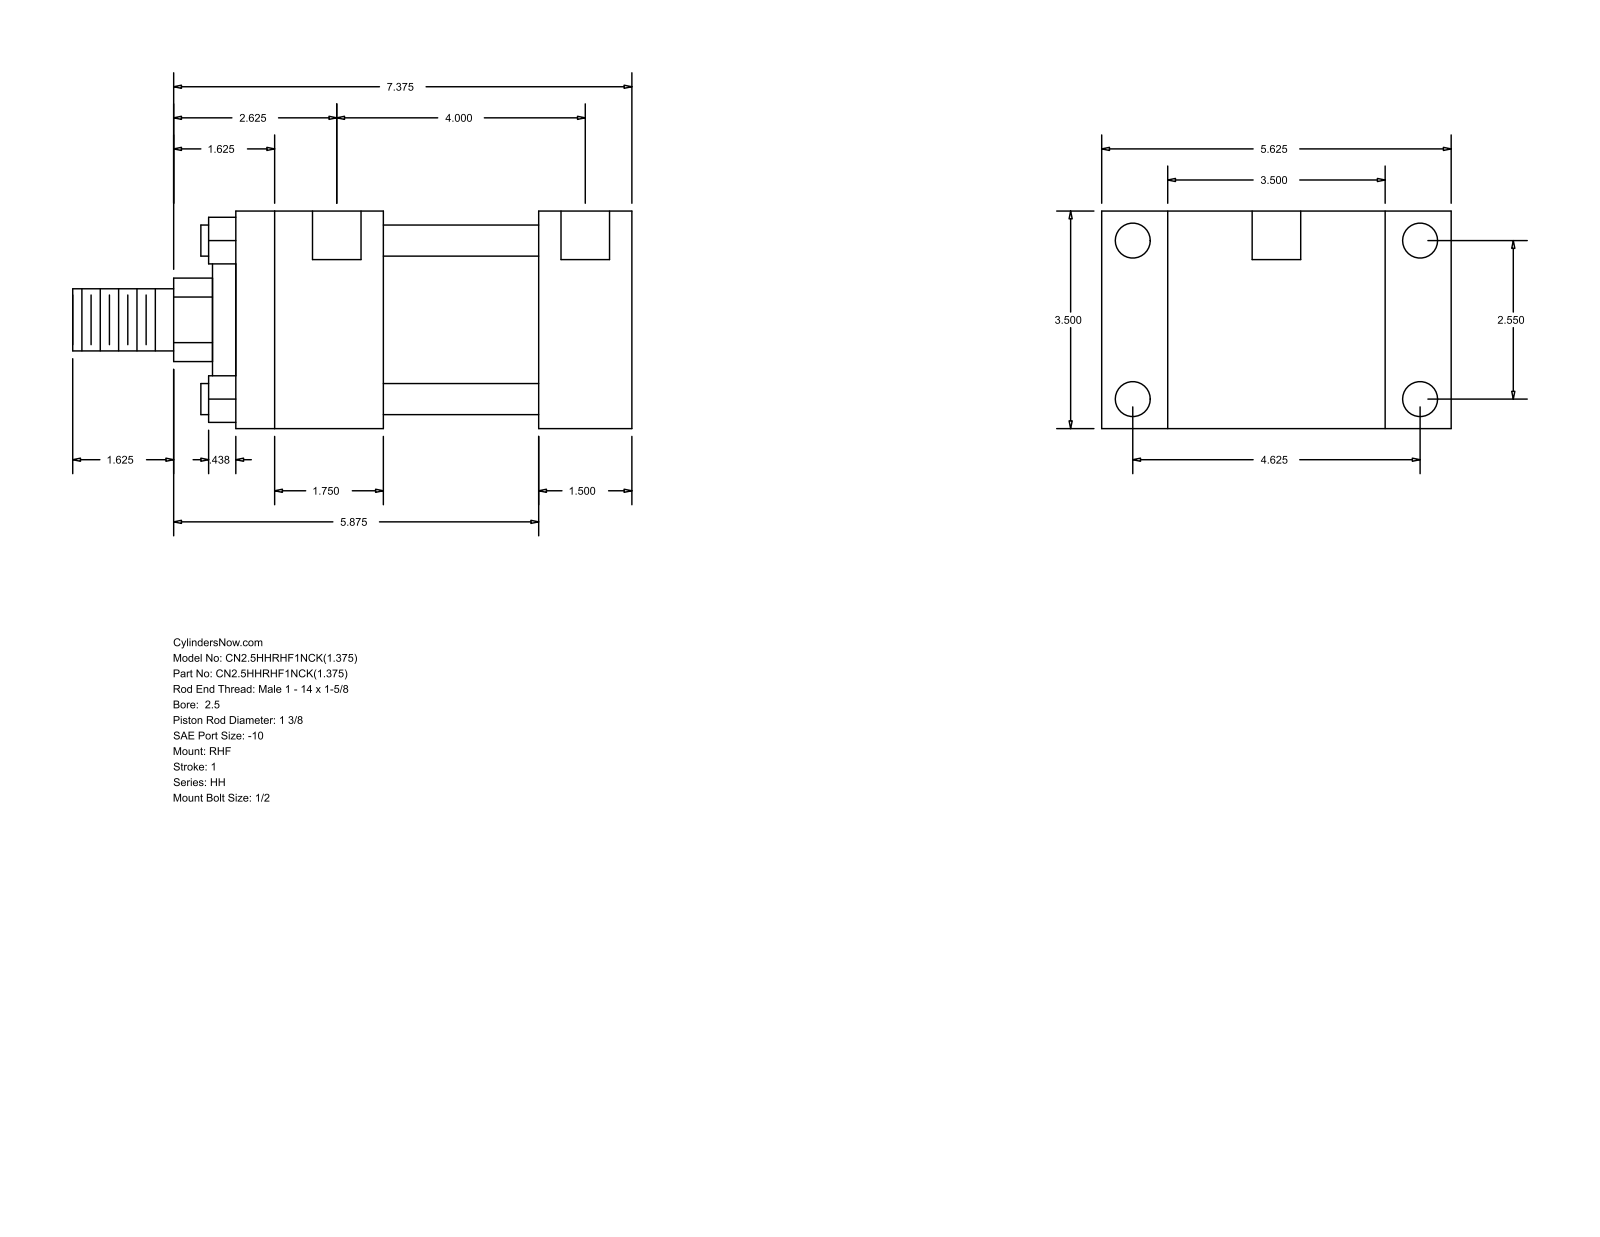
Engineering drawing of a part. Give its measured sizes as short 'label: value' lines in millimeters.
name: HH_RHF__0250_1.375
written by: GSSL Pune (CONFIG_CONTROL_DESIGN)
unit: mm
bodies: 0 solids, 88 faces (60 planar, 28 cylindrical, 0 other)
size: 228.6 × 142.88 × 88.9
holes: 4× ⌀5.56, 4× ⌀14.3, 2× ⌀19.84
bosses: 4× ⌀12.7, 1× ⌀73.03, 1× ⌀50.8, 1× ⌀34.92, 1× ⌀25.4
rounds: 1× R17.06
face distances: 88.9, 38.1, 26.99, 115.89, 123.82, 161.92, 142.88, 60.32, 63.5, 101.6
hole spacings: 1.58, 64.76, 103.19, 104.77, 117.48, 134.15, 101.61
